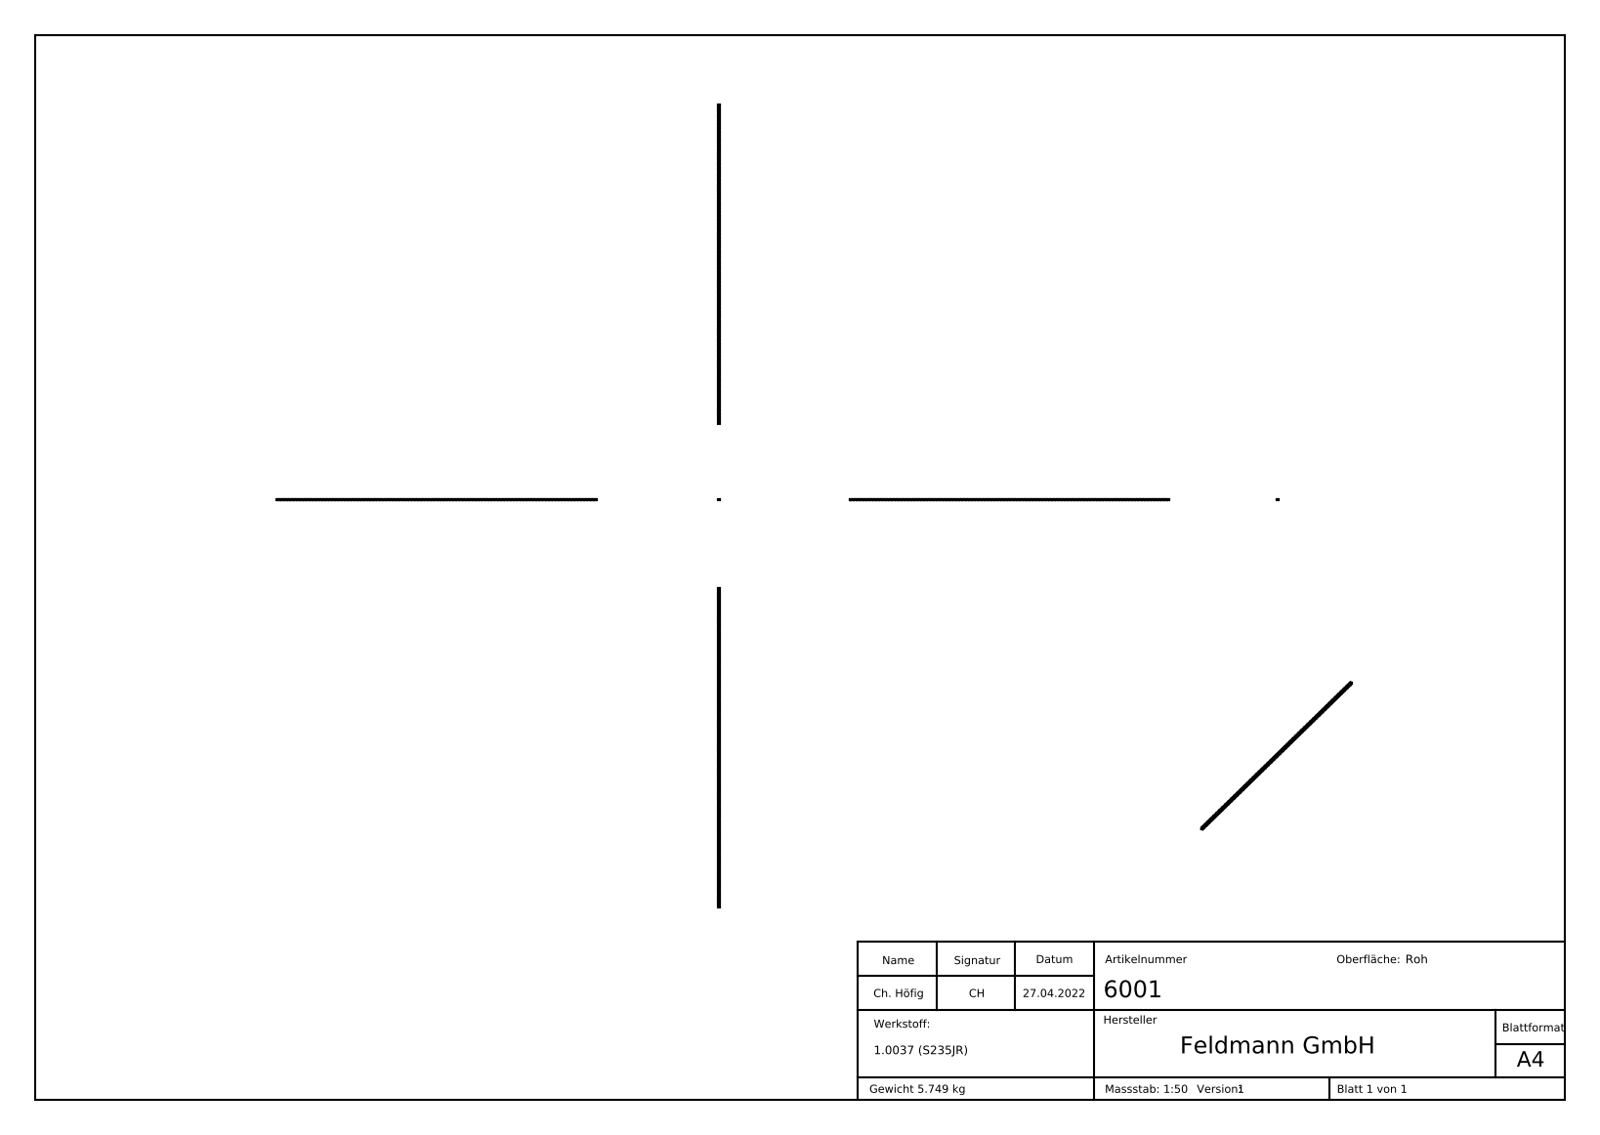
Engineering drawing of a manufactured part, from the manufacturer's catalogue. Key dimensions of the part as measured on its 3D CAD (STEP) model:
Part name (STEP PRODUCT): 6001
STEP written by: SolidWorks 2018 (CONFIG_CONTROL_DESIGN)
Units: millimetres
Bodies: 1 solid, 607 faces (110 planar, 0 cylindrical, 497 other)
Overall size (bounding box): 3000 × 16 × 16
Volume: 737 076 mm³ · Surface area: 186 398 mm²
Main face-to-face distances: 16, 3000, 15.9, 2.21, 0.39, 2.84, 0.34, 1500, 6.99, 9.01
